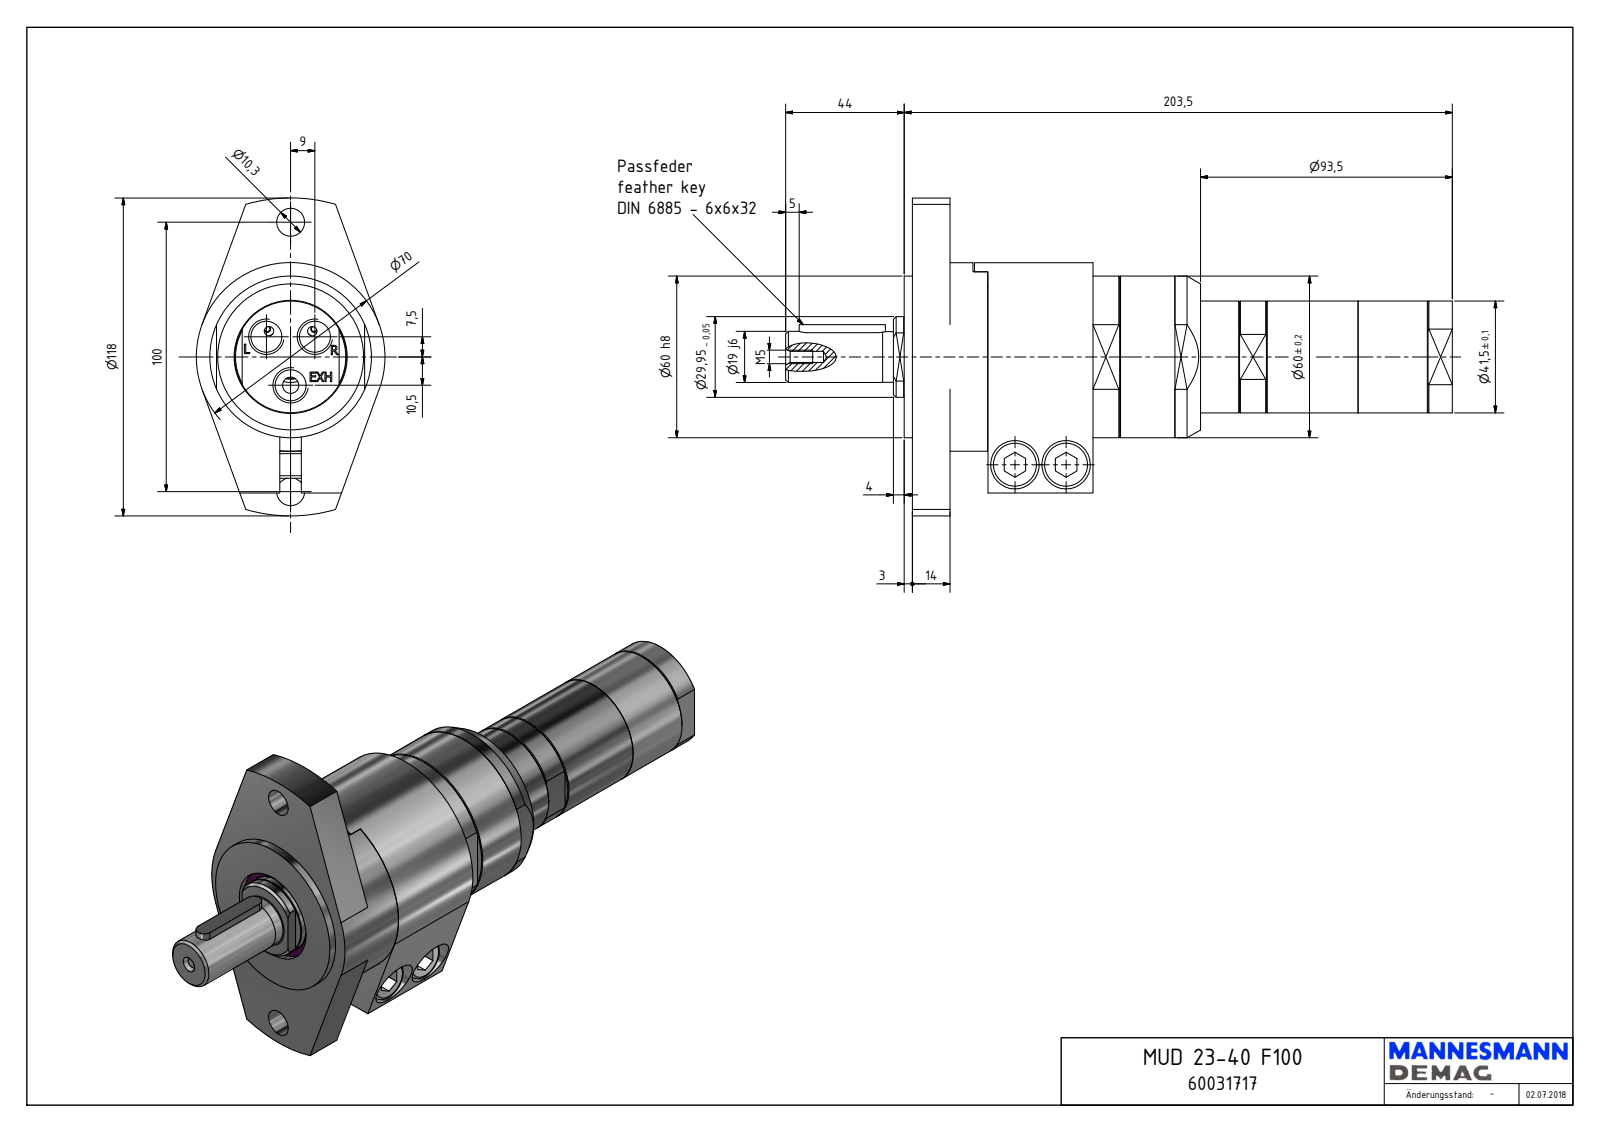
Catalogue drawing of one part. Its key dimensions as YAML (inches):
part_name: "MUD 23-40 F100_60031717"
step_written_by: "Autodesk Inventor 2018 (AUTOMOTIVE_DESIGN)"
units: inches
bodies: {solids: 1, faces: 233, planar: 144, cylindrical: 48, other: 41}
overall_size: [9.744, 4.646, 2.756]
volume: 34.66
surface_area: 101.9
round_holes:
  - {diameter: 0.451, count: 3}
  - {diameter: 0.33, count: 2}
  - {diameter: 0.406, count: 2}
  - {diameter: 0.413, count: 2}
  - {diameter: 0.709, count: 2}
  - {diameter: 0.163, count: 1}
  - {diameter: 1.378, count: 1}
  - {diameter: 1.654, count: 1}
round_bosses_or_shafts:
  - {diameter: 0.63, count: 2}
  - {diameter: 0.394, count: 2}
  - {diameter: 2.756, count: 1}
  - {diameter: 2.431, count: 1}
  - {diameter: 2.362, count: 1}
  - {diameter: 2.172, count: 1}
  - {diameter: 1.634, count: 1}
  - {diameter: 1.179, count: 1}
partial_cylinders:
  - {radius: 0.118, count: 2}
  - {radius: 2.323, count: 1}
face_to_face_distances: [0.551, 0.669, 0.118, 2.76, 2.642, 2.091, 1.535, 1.224, 1.106, 0.555]
hole_center_spacings: [0.461, 0.792, 1.71, 1.969, 2.291, 0.413, 0.709, 0.748]
